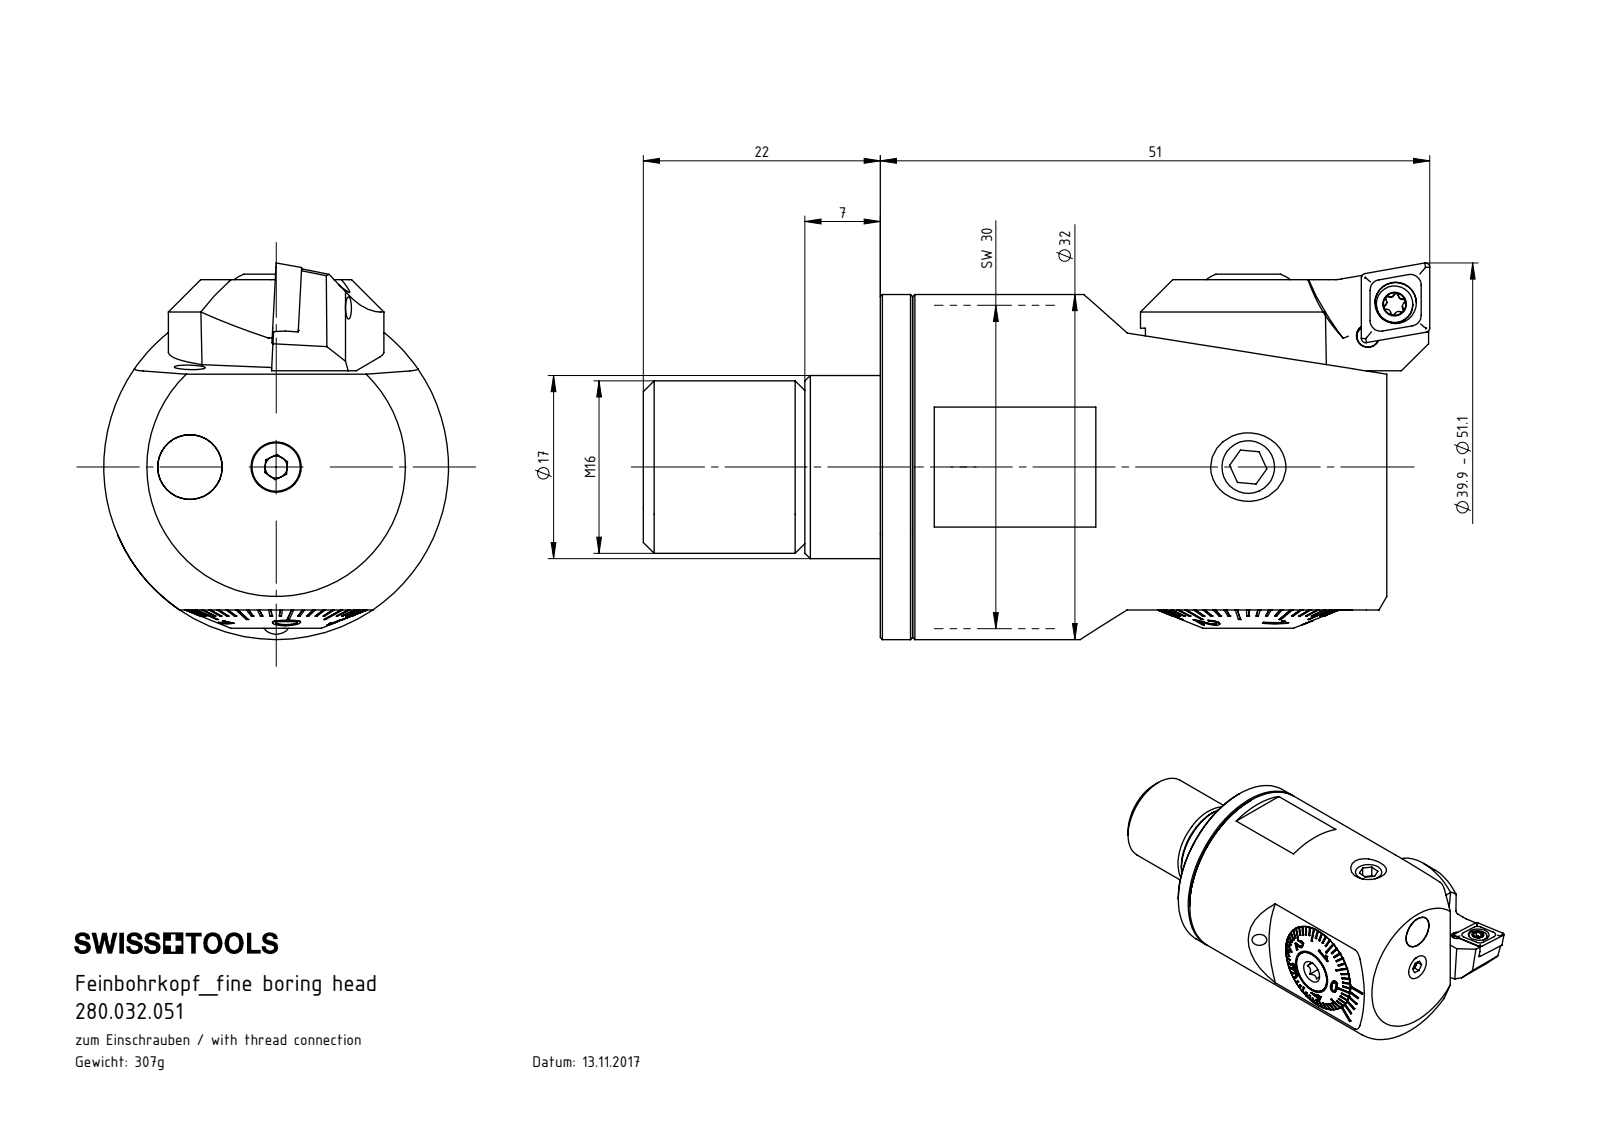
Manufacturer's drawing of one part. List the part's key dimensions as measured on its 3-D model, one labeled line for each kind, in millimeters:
Part name (STEP PRODUCT): F32-BG1.002.017_B; 280.032.051; F32-BG3.006.026_A; T7 M2.5 x 6 (+8 more)
STEP written by: SolidWorks 2017 (CONFIG_CONTROL_DESIGN)
Units: millimetres
Bodies: 20 solids, 837 faces (363 planar, 158 cylindrical, 316 other)
Overall size (bounding box): 73 × 34.94 × 32
Volume: 39 272 mm³ · Surface area: 20 275 mm²
Round holes (diameter × count): ⌀2.5 ×5, ⌀5 ×2, ⌀17 ×2, ⌀2 ×1, ⌀2.05 ×1, ⌀2.1 ×1, ⌀2.7 ×1, ⌀2.8 ×1, ⌀2.9 ×1, ⌀3 ×1, ⌀3.3 ×1, ⌀3.85 ×1
Round bosses / shafts (diameter × count): ⌀6 ×2, ⌀2.5 ×2, ⌀32 ×1, ⌀16.98 ×1, ⌀16.85 ×1, ⌀16 ×1, ⌀14.65 ×1, ⌀12 ×1
Partial cylindrical surfaces — rounded edges, fillets, slot ends (radius × count): R0.21 ×6, R0.36 ×5, R0.5 ×4, R1.75 ×2, R0.36 ×1, R1 ×1, R1.07 ×1, R1.9 ×1
Main face-to-face distances: 3, 47, 44, 4.5, 25.14, 30, 8, 0.8, 1.5, 3.7
Hole centre spacings: 3.84, 3.99, 5.7, 8, 11.68, 24.15
